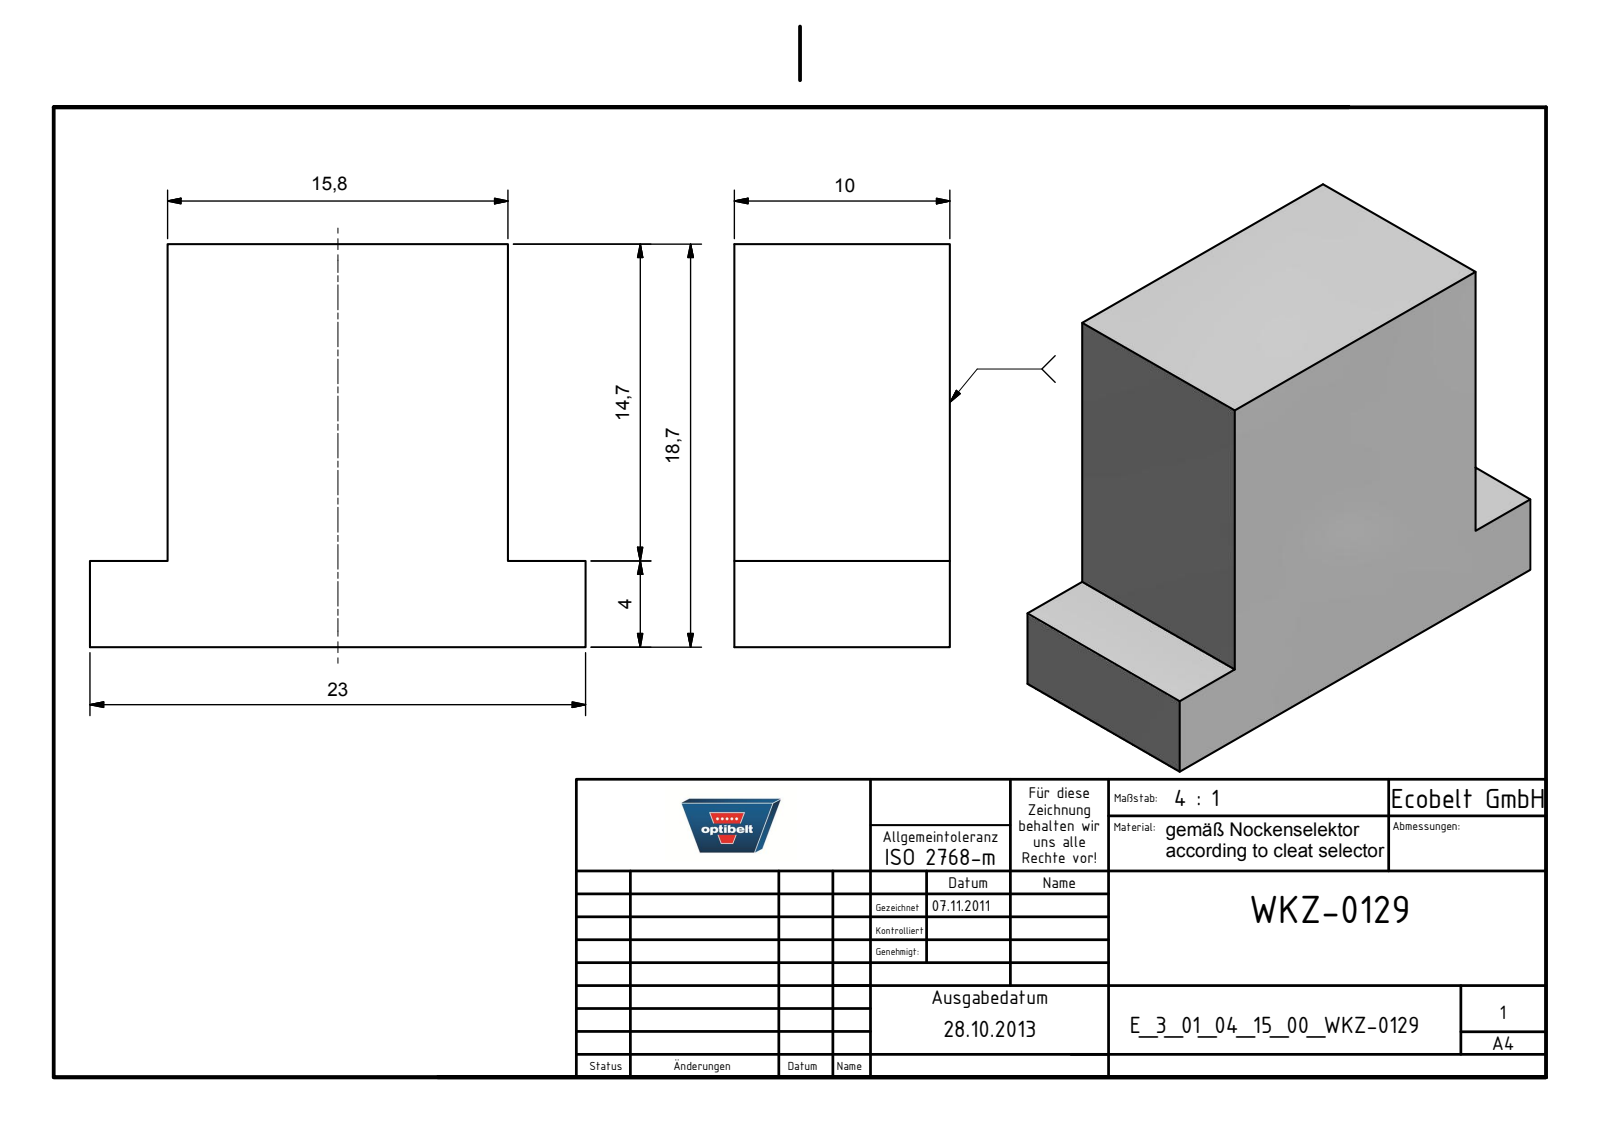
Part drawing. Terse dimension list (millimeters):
name: E_3_01_04_15_00_WKZ-0129
written by: Autodesk Inventor 2025 (AUTOMOTIVE_DESIGN)
unit: mm
bodies: 1 solid, 10 faces (10 planar, 0 cylindrical, 0 other)
size: 23 × 18.7 × 10
volume: 3 243 mm³; area: 1 483 mm²
face distances: 10, 18.7, 15.8, 3.6, 19.4, 4, 14.7, 23
